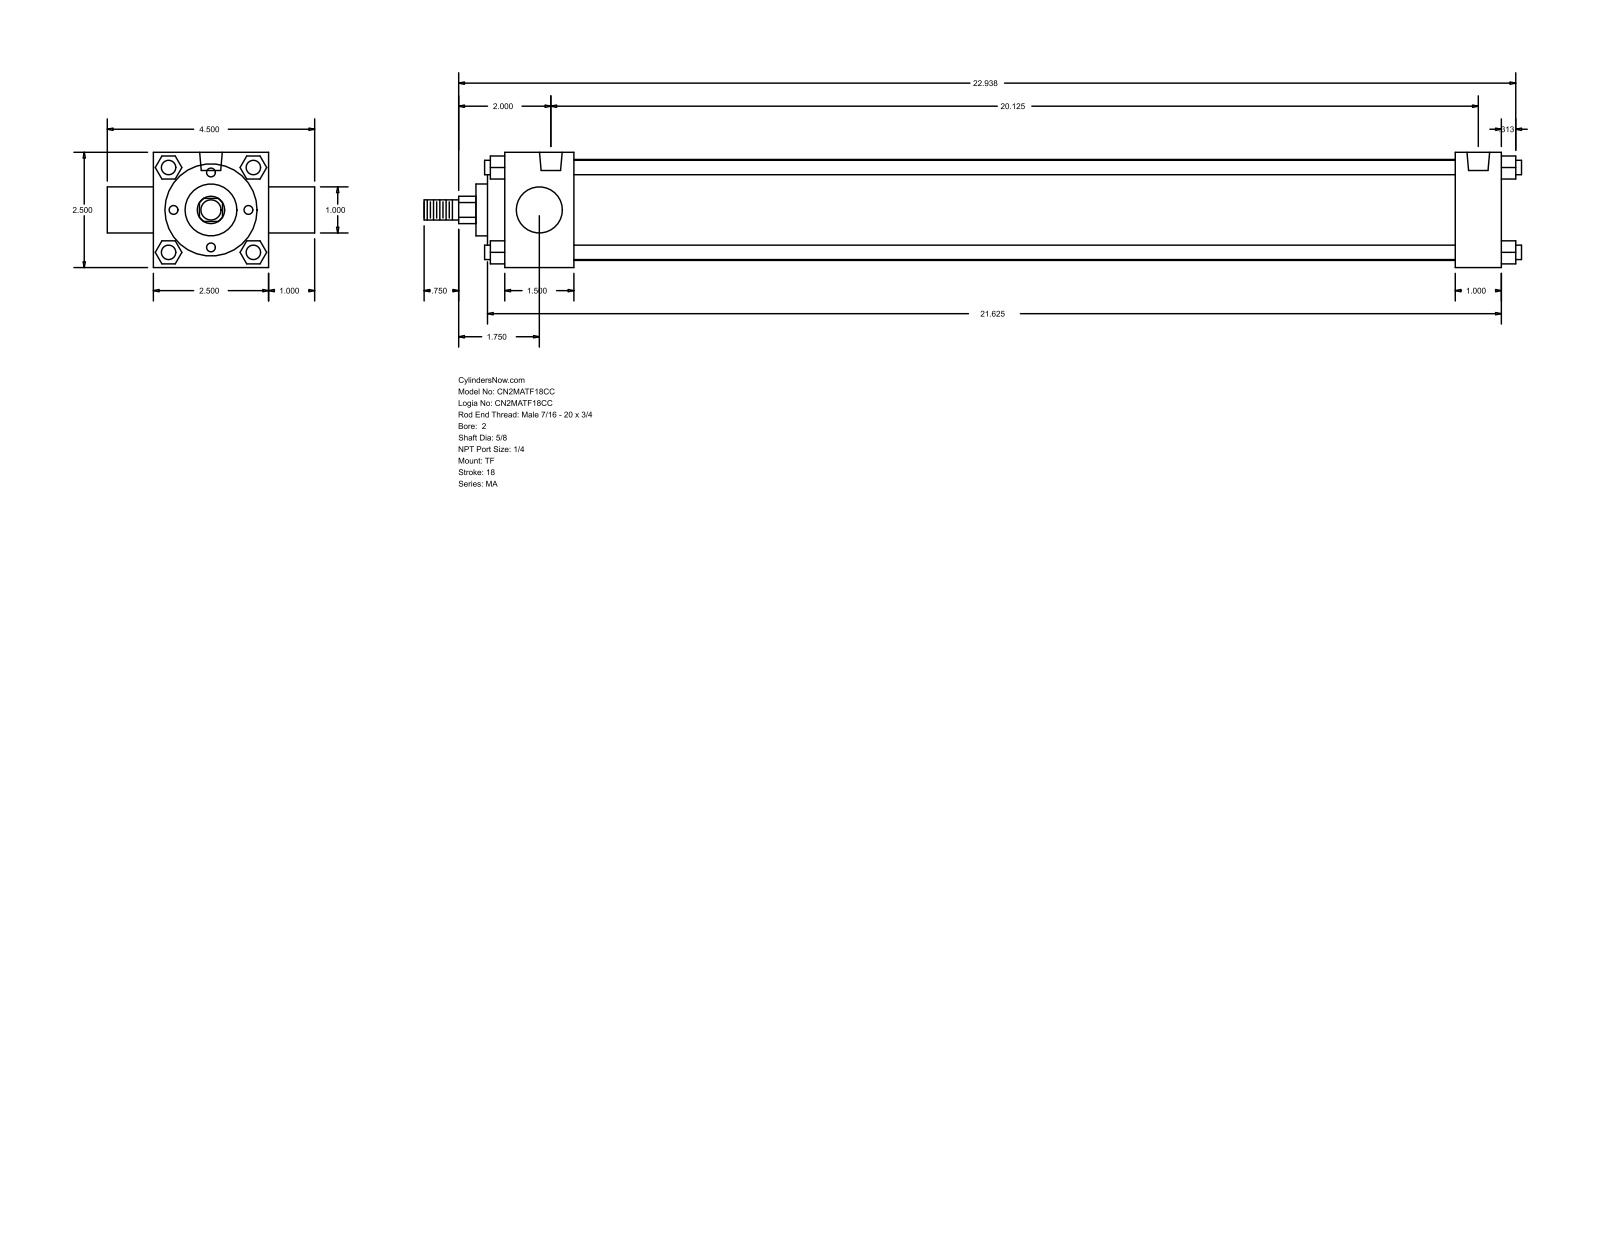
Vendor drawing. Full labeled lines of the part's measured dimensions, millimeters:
Part name (STEP PRODUCT): MA_TF__0200_0.625
STEP written by: GSSL Pune (CONFIG_CONTROL_DESIGN)
Units: millimetres
Bodies: 0 solids, 122 faces (93 planar, 29 cylindrical, 0 other)
Overall size (bounding box): 604.84 × 114.3 × 63.5
Round holes (diameter × count): ⌀7.94 ×3, ⌀12.49 ×2
Round bosses / shafts (diameter × count): ⌀7.94 ×4, ⌀55.63 ×1, ⌀50.8 ×1, ⌀28.57 ×1, ⌀25.4 ×1, ⌀15.88 ×1, ⌀11.11 ×1
Partial cylindrical surfaces — rounded edges, fillets, slot ends (radius × count): R7.54 ×1
Main face-to-face distances: 63.5, 25.4, 38.1, 549.27, 12.7, 523.87, 485.77, 511.17, 9.52, 47.62
Hole centre spacings: 511.18
